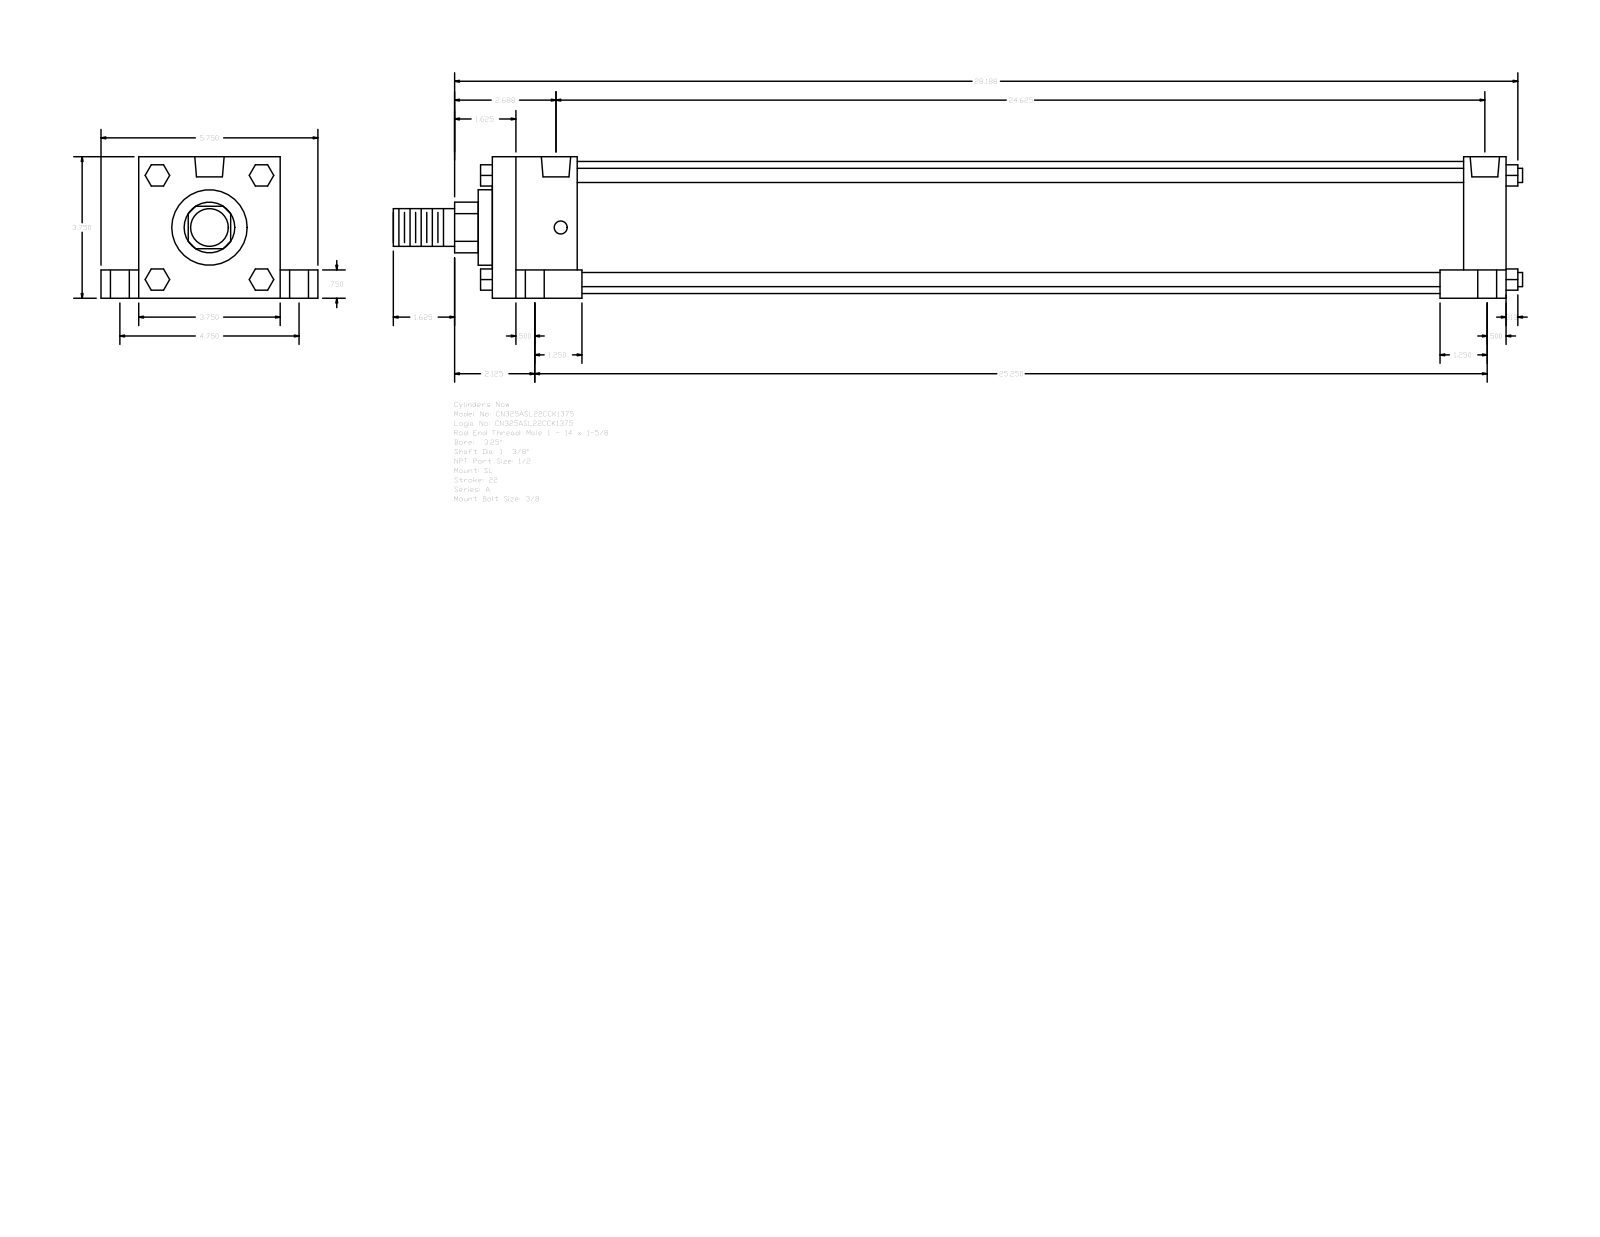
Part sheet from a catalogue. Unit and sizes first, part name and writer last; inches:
Units: inches
Overall size (bounding box): 29.937 × 5.75 × 3.75
Round holes (diameter × count): ⌀0.344 ×4, ⌀0.5 ×4, ⌀0.75 ×4, ⌀0.778 ×2
Round bosses / shafts (diameter × count): ⌀0.375 ×4, ⌀3.5 ×1, ⌀2 ×1, ⌀1.375 ×1, ⌀1 ×1
Partial cylindrical surfaces — rounded edges, fillets, slot ends (radius × count): R0.672 ×1
Main face-to-face distances: 3.75, 26.875, 1, 4.75, 0.75, 3, 2.25, 1.125, 25.75, 23.5
Hole centre spacings: 0.125, 2.376, 2.383, 2.441, 2.473, 4.75, 24.375, 24.5
Bodies: 0 solids, 150 faces (114 planar, 36 cylindrical, 0 other)
Part name (STEP PRODUCT): A_SL__0325_1.375
STEP written by: GSSL Pune (CONFIG_CONTROL_DESIGN)
